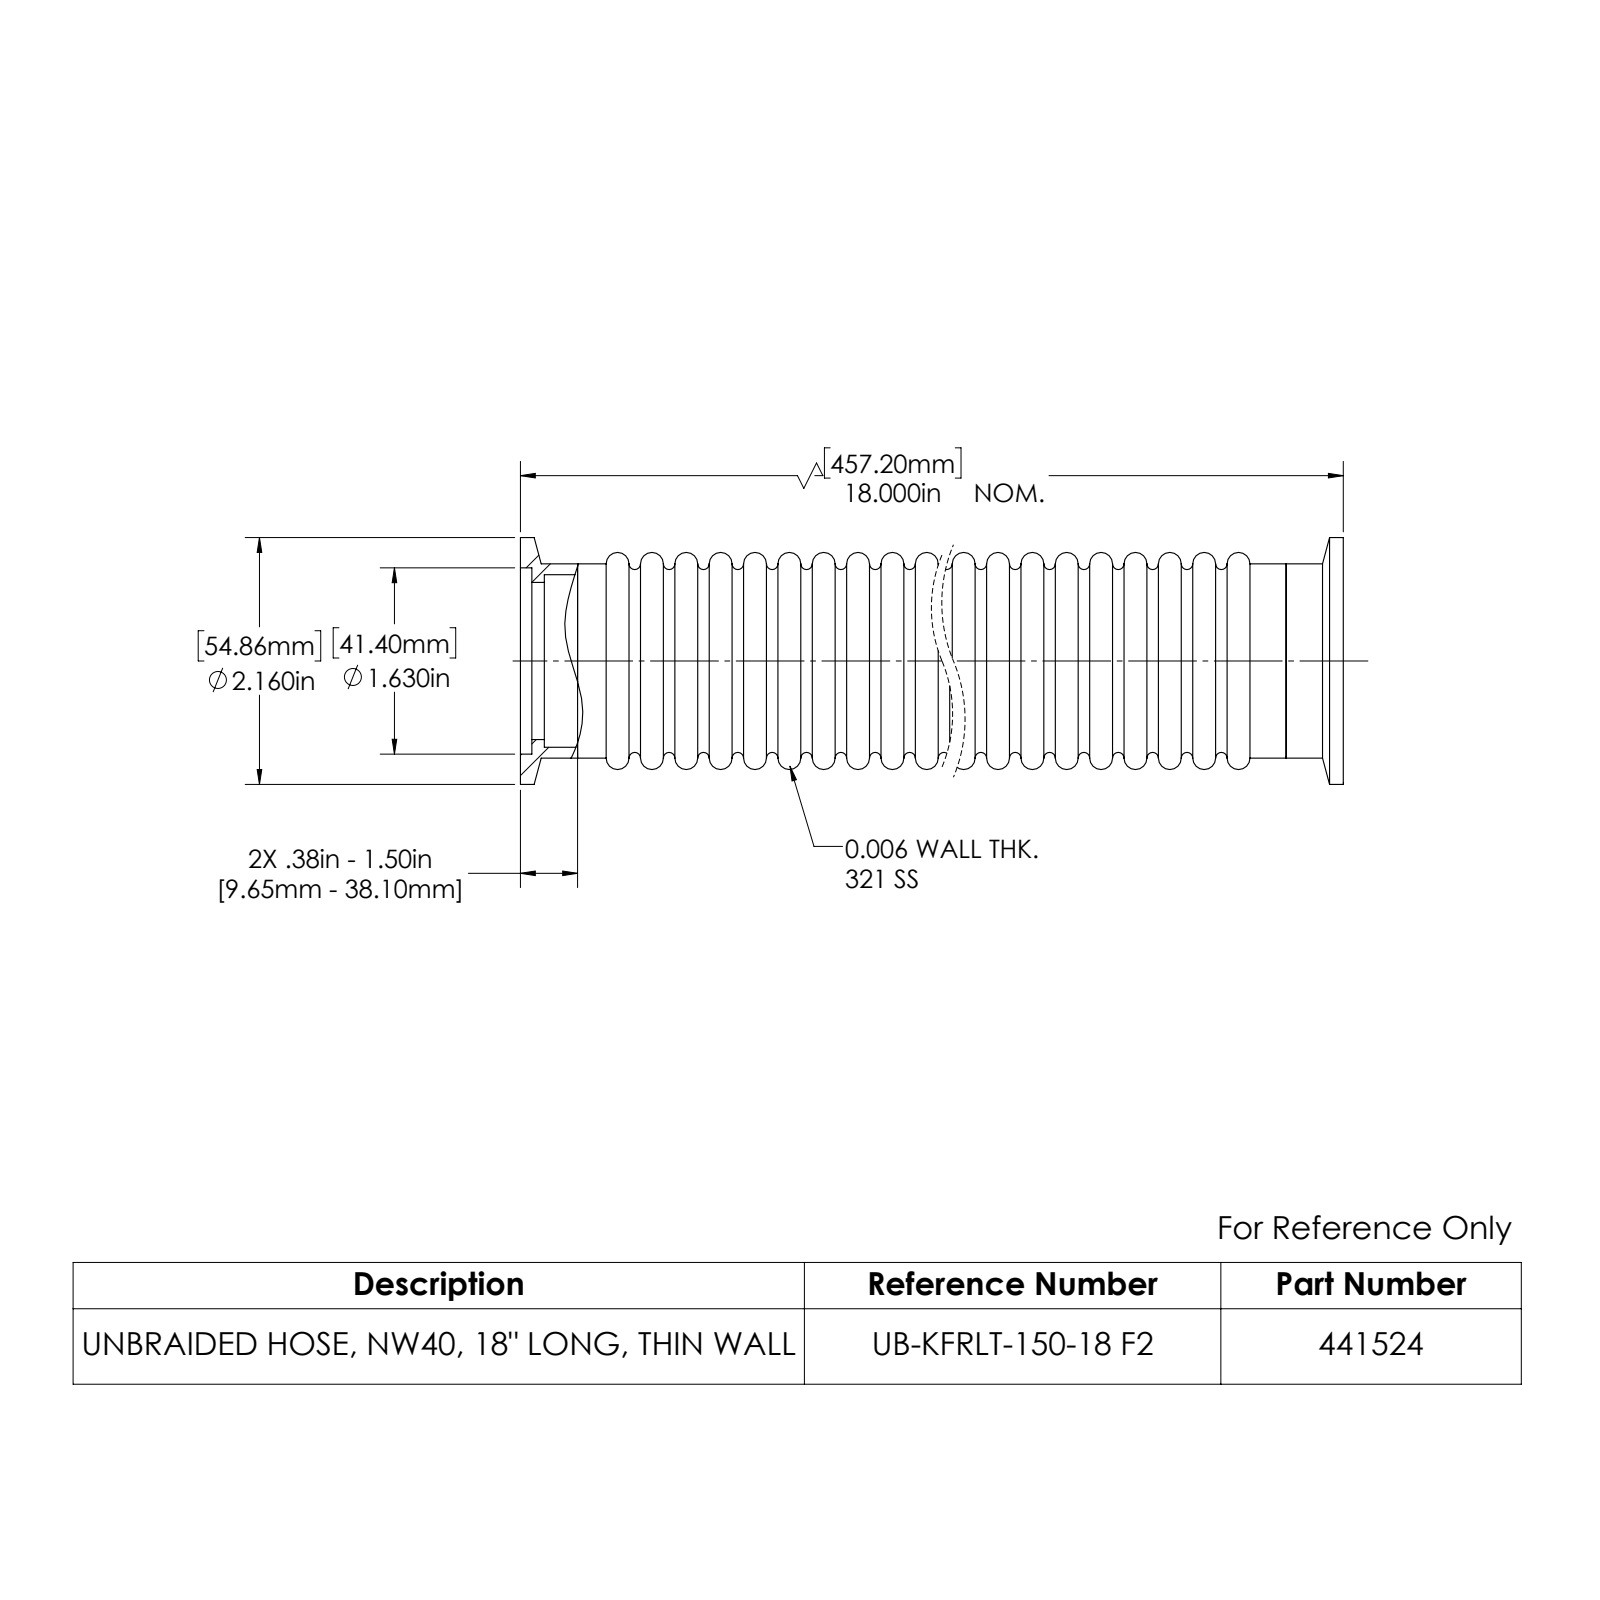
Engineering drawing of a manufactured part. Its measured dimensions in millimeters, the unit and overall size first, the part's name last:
Units: millimetres
Overall size (bounding box): 457.2 × 54.9 × 54.9
Round holes (diameter × count): ⌀34.9 ×1, ⌀38.4 ×1, ⌀41.4 ×1, ⌀41.7 ×1
Round bosses / shafts (diameter × count): ⌀54.9 ×1, ⌀43.2 ×1
Main face-to-face distances: 457.2, 12.7, 444.5, 2.5, 454.7, 10.2, 442, 431.8, 5.3, 451.9
Volume: 85 110 mm³ · Surface area: 196 800 mm²
Bodies: 3 solids, 694 faces (10 planar, 28 cylindrical, 656 other)
Part name (STEP PRODUCT): 441540; 713003; 441524_B
STEP written by: SolidWorks 2022 (CONFIG_CONTROL_DESIGN)
